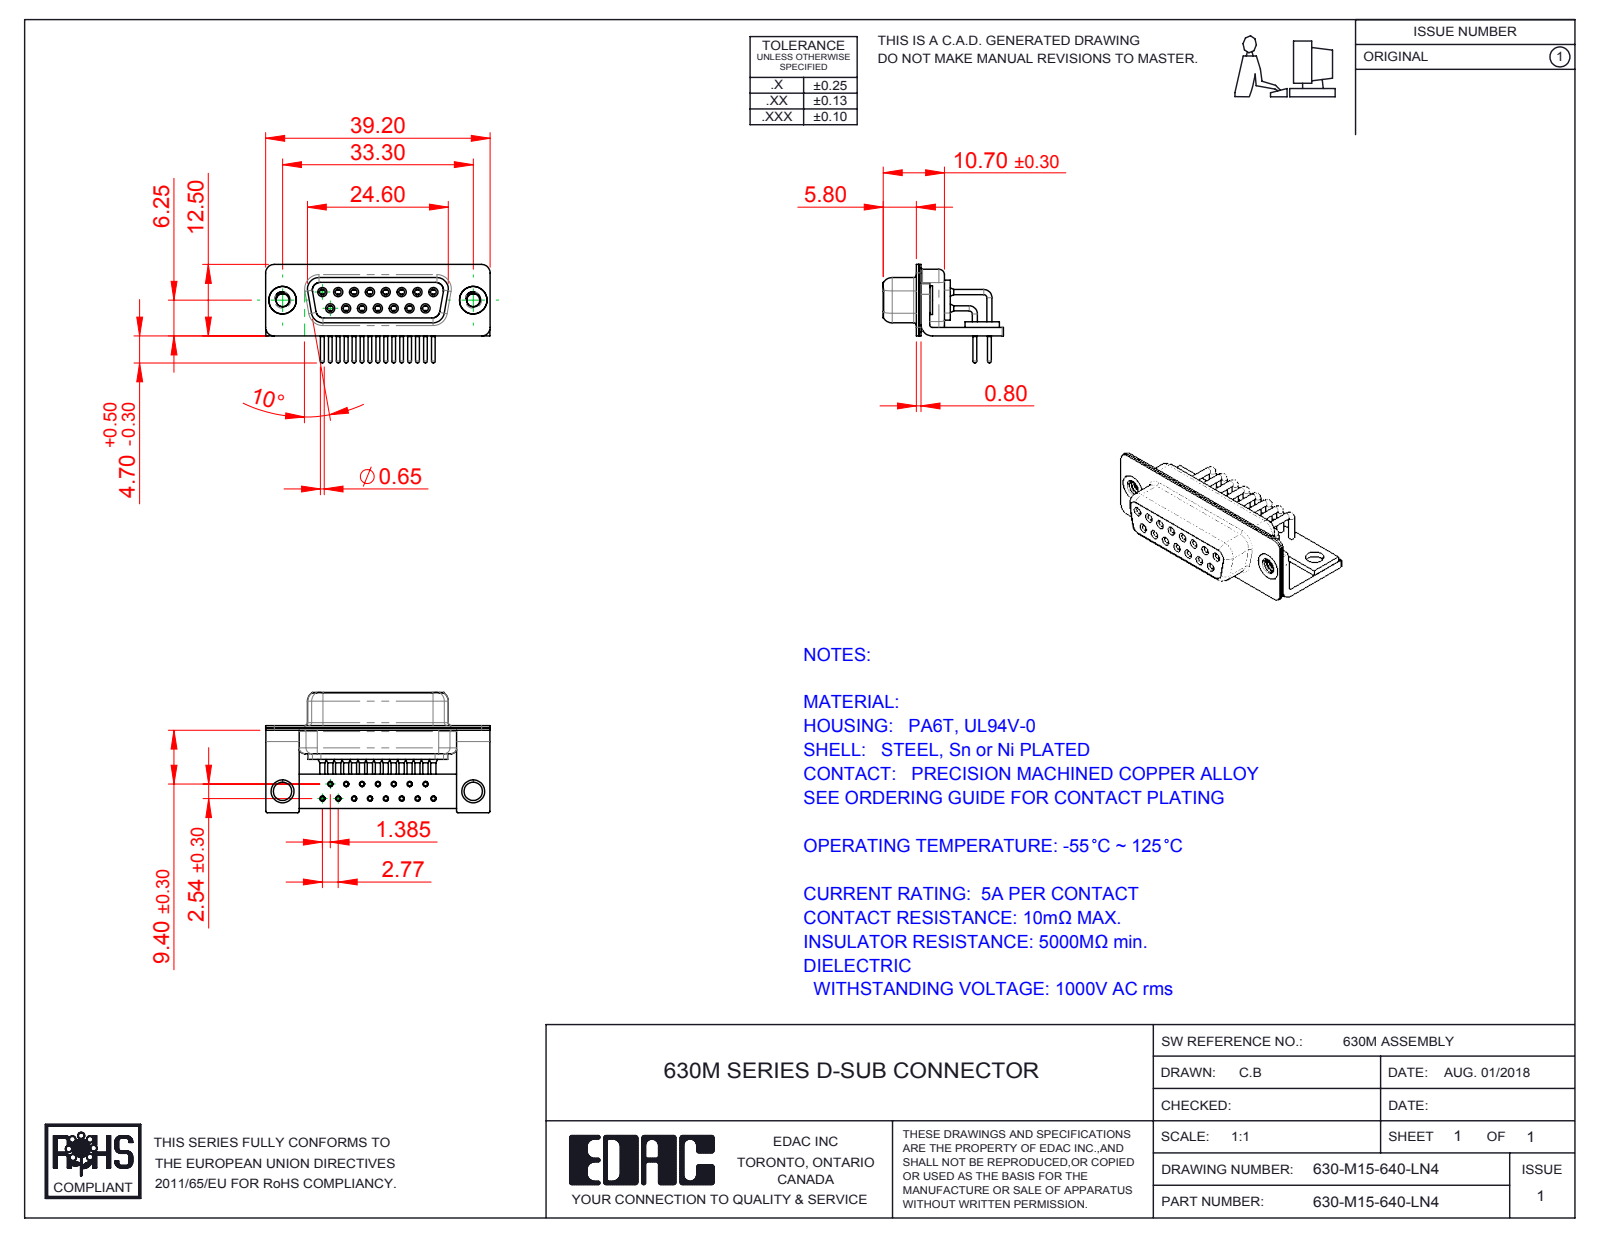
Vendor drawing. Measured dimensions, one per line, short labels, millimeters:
name: 630M Stabilizer Board_15 Contacts; 630M Contact Row 2; 630M Shell Front_15 Contacts; 630M Stabilizer Bracket (+5 more)
written by: SolidWorks 2016 (CONFIG_CONTROL_DESIGN)
unit: mm
bodies: 23 solids, 1154 faces (318 planar, 534 cylindrical, 302 other)
size: 39.2 × 21 × 17.2
volume: 3 044 mm³; area: 7 715 mm²
holes: 15× ⌀0.9, 15× ⌀1, 15× ⌀1.1, 15× ⌀1.7, 15× ⌀1.8, 15× ⌀2, 2× ⌀2.26, 2× ⌀3.2, 2× ⌀4, 2× ⌀4.8
bosses: 27× ⌀0.9, 15× ⌀1.6, 15× ⌀1.5, 15× ⌀0.65, 2× ⌀5, 2× ⌀4.9
rounds: 16× R0.25, 16× R1.5, 13× R2, 8× R1.35, 8× R1.6, 5× R0.5, 4× R0.6, 4× R0.65
face distances: 0.4, 0.8, 2.3, 9.35, 1.9, 1.5, 1, 1.45, 8.95, 0.85
hole spacings: 2.77, 5.54, 8.31, 3.16, 4.87, 11.08, 2.89, 7.37
